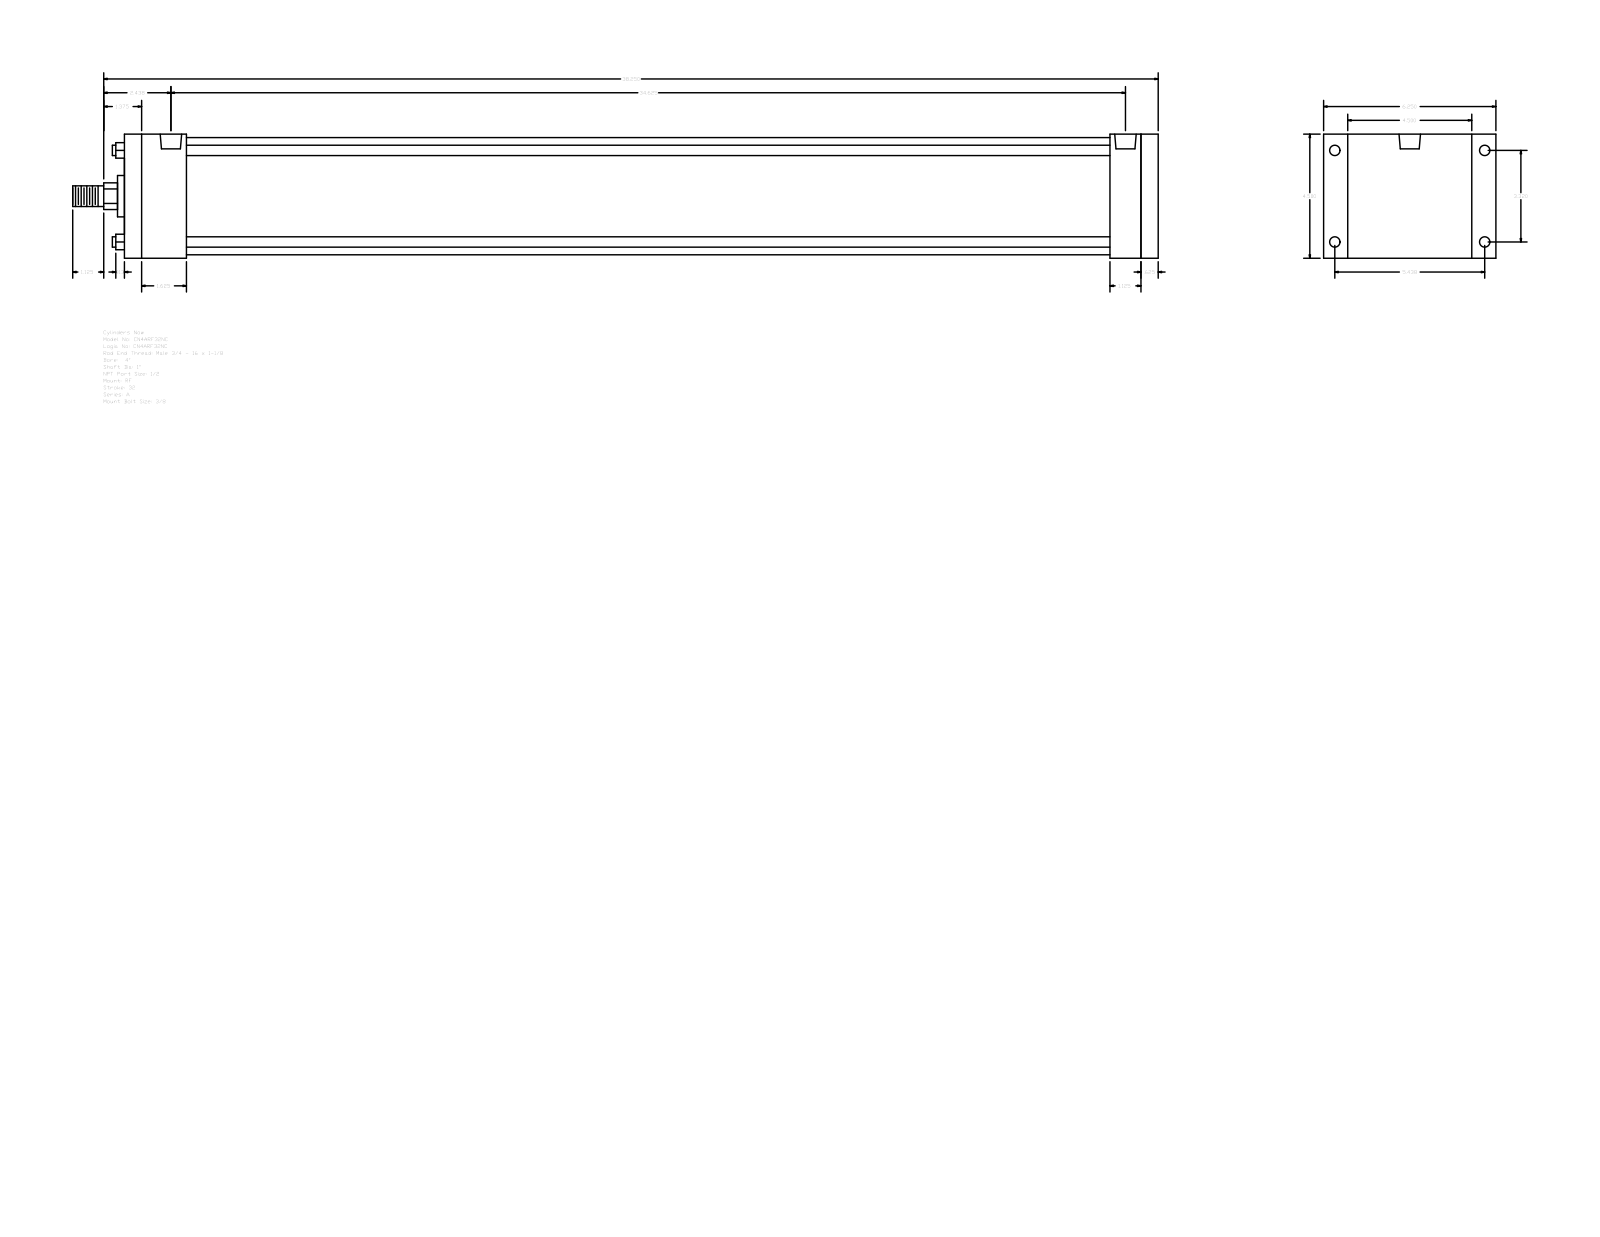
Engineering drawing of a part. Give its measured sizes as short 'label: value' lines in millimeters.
name: A_RF__0400_1
written by: GSSL Pune (CONFIG_CONTROL_DESIGN)
unit: mm
bodies: 0 solids, 92 faces (64 planar, 28 cylindrical, 0 other)
size: 1000.12 × 158.75 × 114.3
holes: 4× ⌀8.73, 4× ⌀9.53, 2× ⌀19.77
bosses: 4× ⌀9.53, 1× ⌀107.95, 1× ⌀38.1, 1× ⌀25.4, 1× ⌀19.05
rounds: 1× R12.29
face distances: 114.3, 952.5, 936.62, 15.88, 28.57, 22.23, 136.53, 908.05, 44.45, 57.15
hole spacings: 3.18, 84.32, 138.12, 161.82, 873.12, 876.3, 879.48
